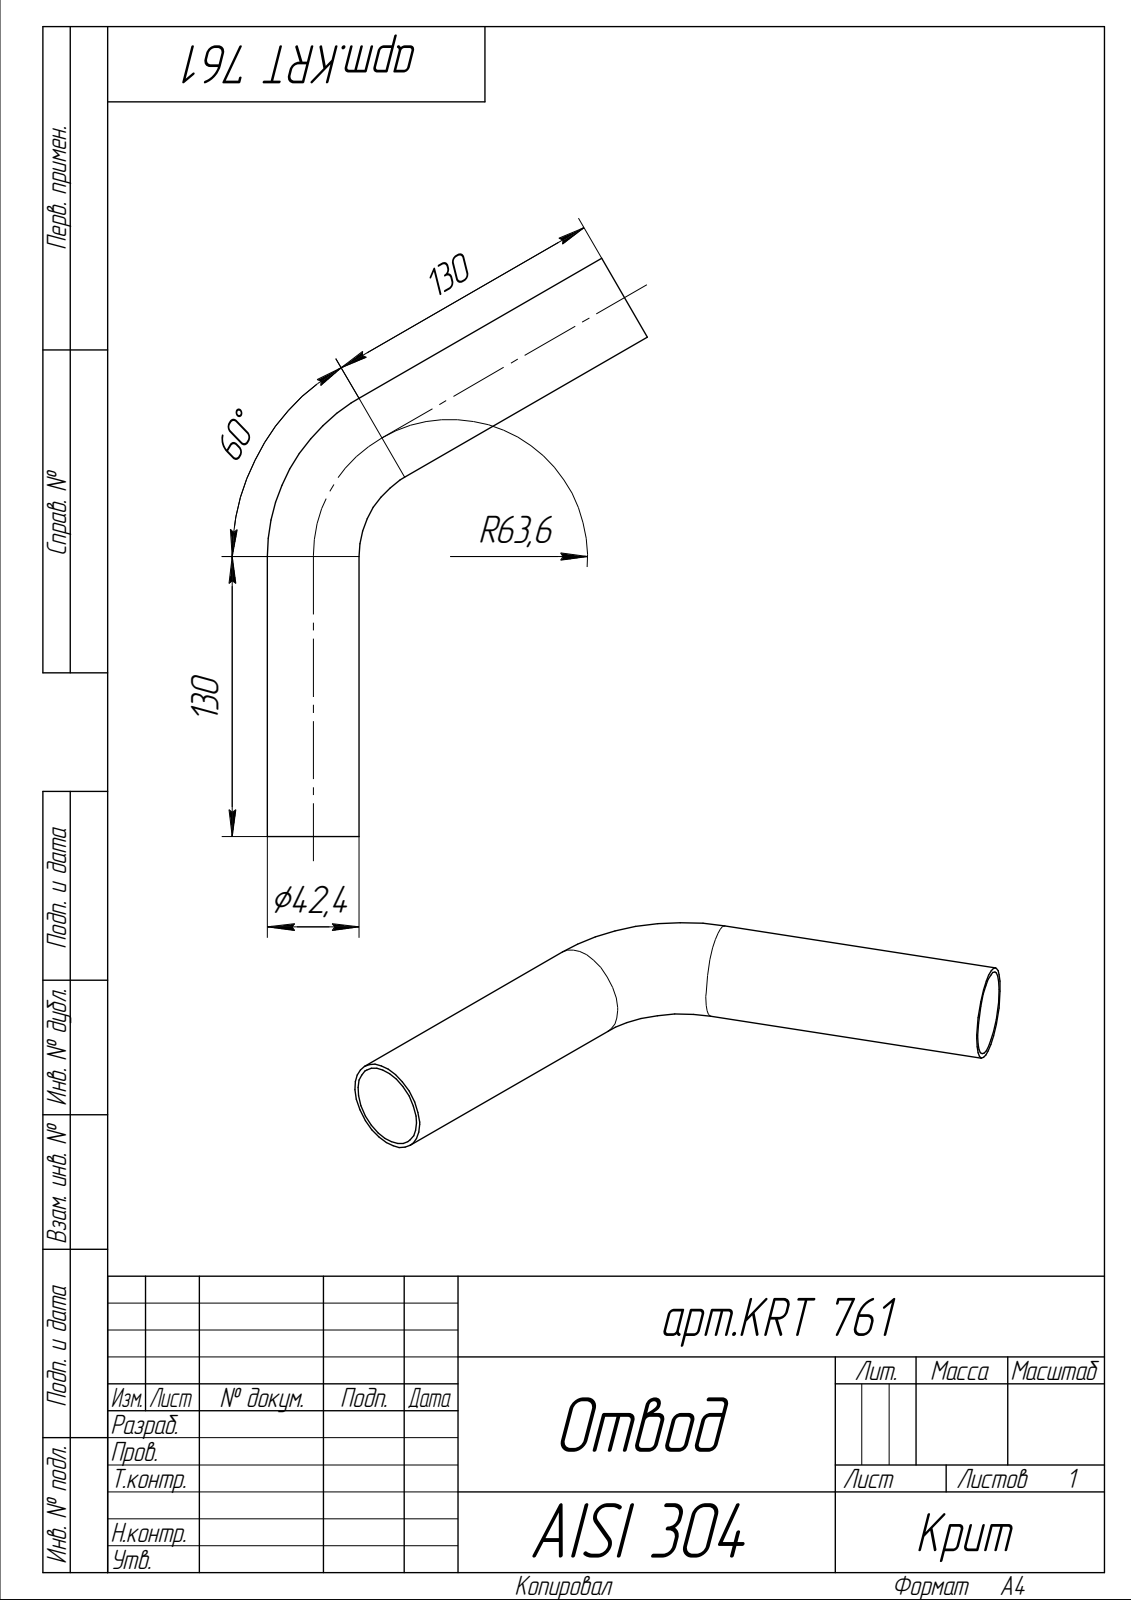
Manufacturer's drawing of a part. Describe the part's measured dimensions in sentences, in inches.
The part is named "Деталь". Its 3-D file was written by "ASCON Math Kernel (AUTOMOTIVE_DESIGN)". It is 1 solid with 8 faces: 2 planar, 4 cylindrical and 2 other. Overall it measures 10.569 by 6.936 by 1.669 inches. Its volume is 5.059 cubic inches and its surface area 129.3 square inches. Round holes: 2 of diameter 1.512. Round bosses or shafts: 2 of diameter 1.669.
